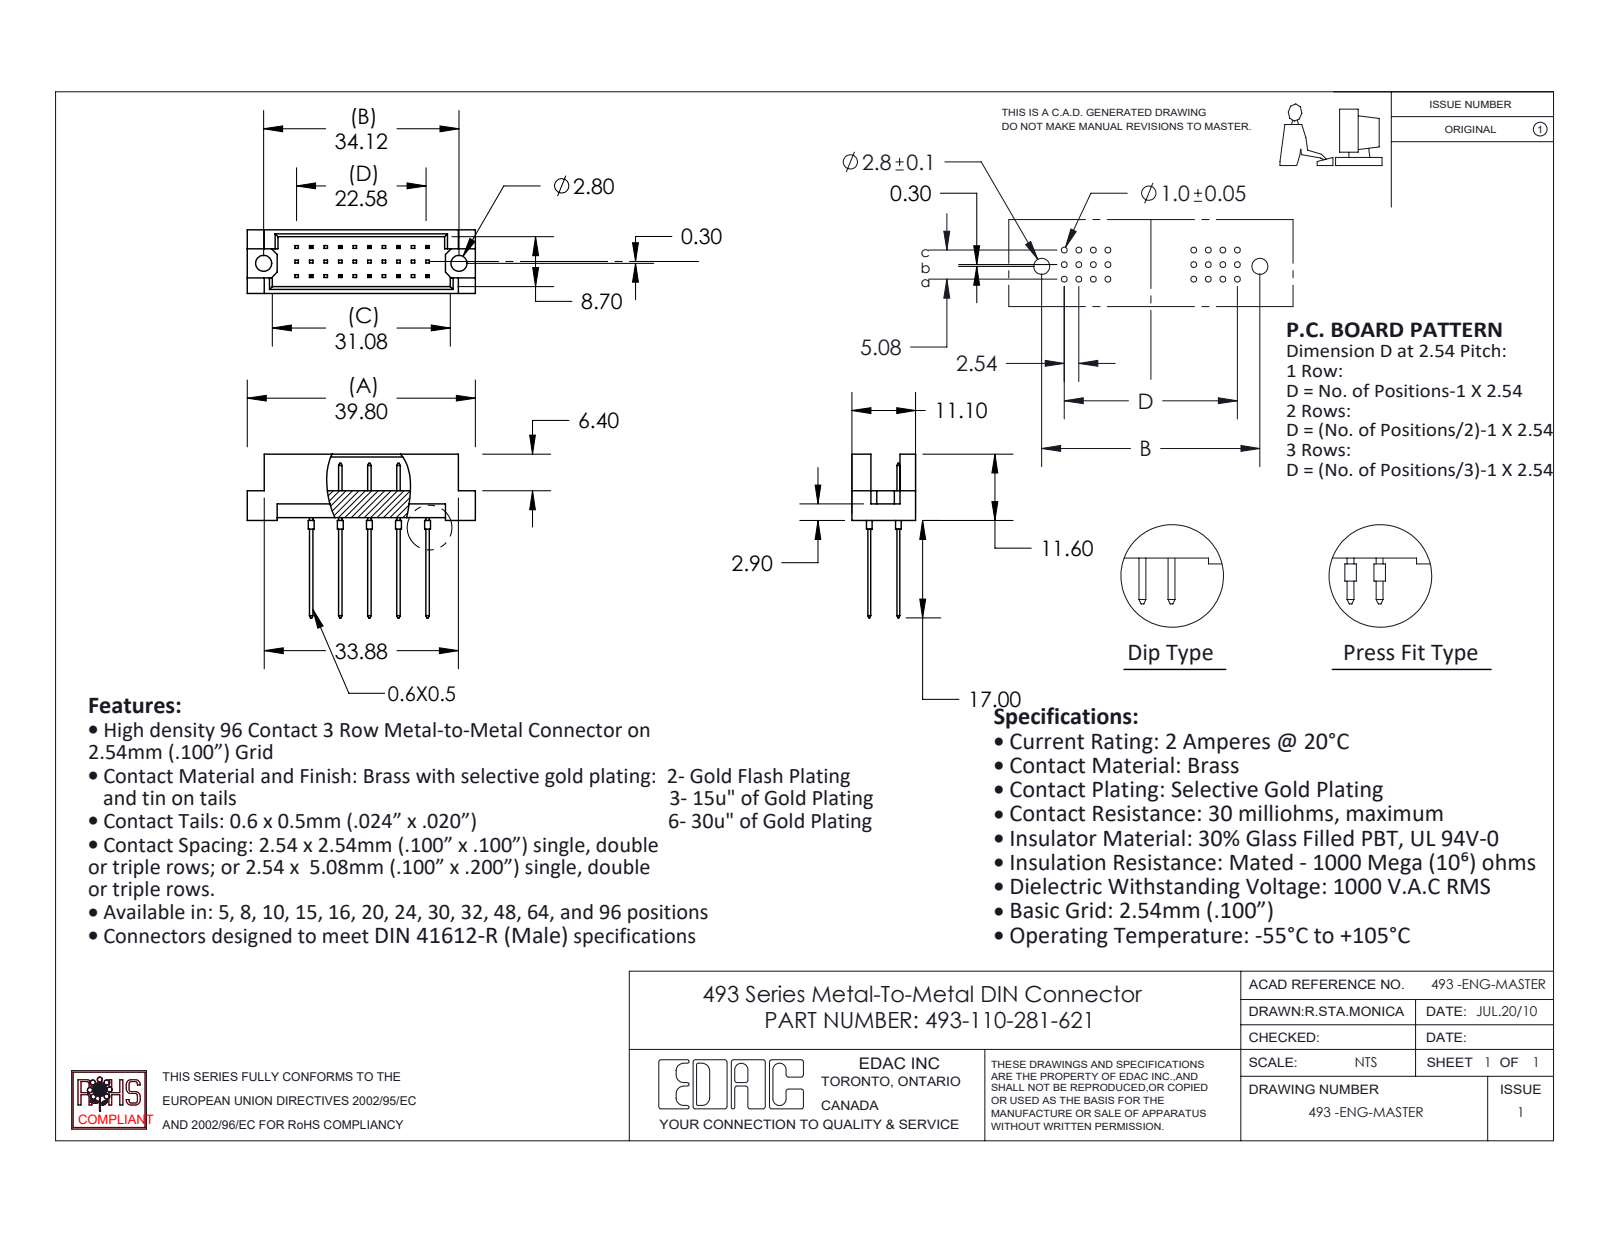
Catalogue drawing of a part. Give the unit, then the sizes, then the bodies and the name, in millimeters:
Units: millimetres
Overall size (bounding box): 39.8 × 28.6 × 11.1
Round holes (diameter × count): ⌀2.8 ×2
Round bosses / shafts (diameter × count): ⌀1 ×10
Main face-to-face distances: 5.08, 1.2, 9.9, 11.1, 0.5, 8.7, 4.7, 2.76, 3.26, 7.84
Hole centre spacings: 34.12
Volume: 2 460 mm³ · Surface area: 3 352 mm²
Bodies: 11 solids, 392 faces (368 planar, 24 cylindrical, 0 other)
Part name (STEP PRODUCT): 493 Part_30; 493-290_81; 493-110-281-622
STEP written by: SolidWorks 2020 (CONFIG_CONTROL_DESIGN)
